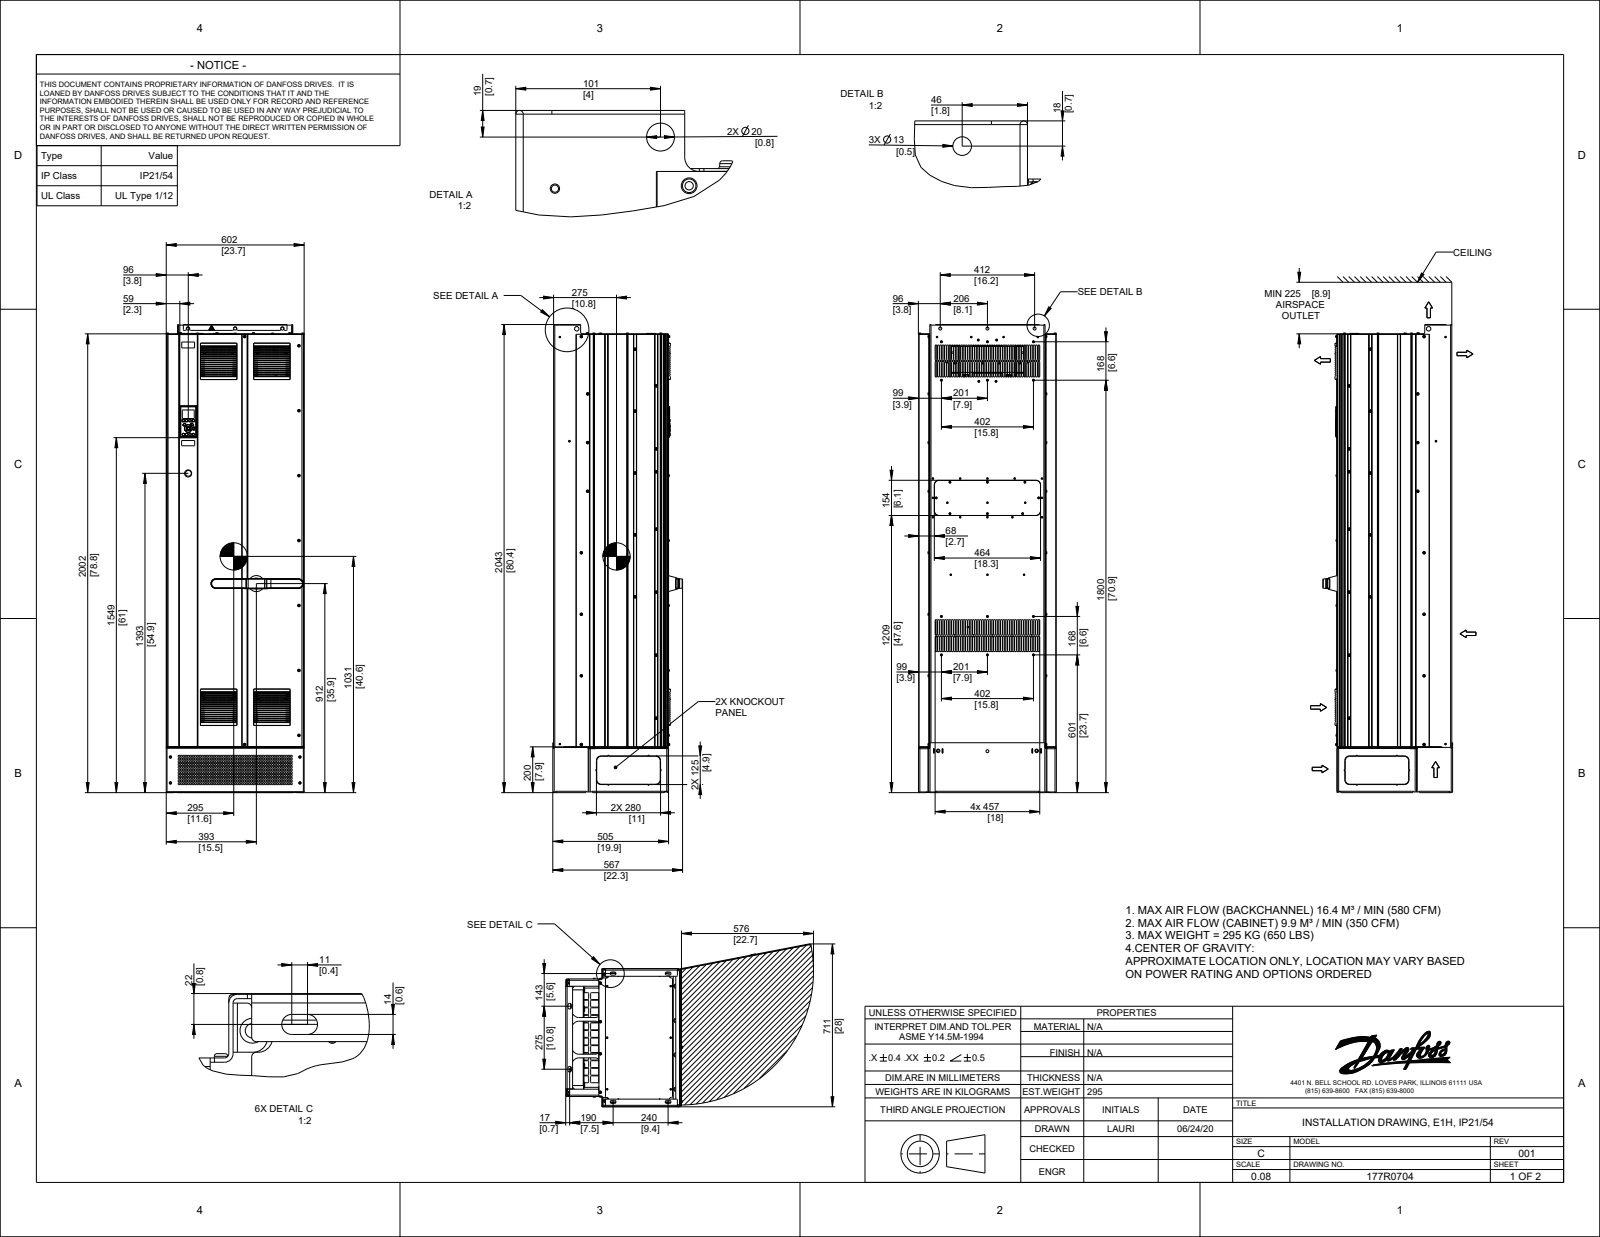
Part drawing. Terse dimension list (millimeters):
name: 177G8943; FH-M6-15-ZI; SS-M5-2-ZI; S-M6-2-ZI (+8 more)
written by: CREO PARAMETRIC BY PTC INC, 2015480 (CONFIG_CONTROL_DESIGN)
unit: mm
bodies: 600 solids, 39457 faces (23407 planar, 9063 cylindrical, 6987 other)
size: 2042.6 × 603 × 514.14
volume: 22 040 000 mm³; area: 17 500 000 mm²
holes: 148× ⌀5, 85× ⌀6, 40× ⌀6.33, 32× ⌀1.2, 30× ⌀5.8, 26× ⌀8, 21× ⌀6.5, 20× ⌀4, 19× ⌀5.5, 17× ⌀6.3, 16× ⌀1.5, 16× ⌀6.4
bosses: 83× ⌀6.5, 60× ⌀8.7, 49× ⌀10.8, 49× ⌀9.8, 46× ⌀12, 28× ⌀5, 26× ⌀11, 20× ⌀6.33
rounds: 456× R4, 369× R0.5, 325× R3.2, 243× R1, 134× R0.4, 122× R0.3, 105× R1.6, 86× R2
face distances: 3, 2.6, 494.36, 497.36, 496.96, 499.96, 597.1, 1.9, 6.4, 590.7
hole spacings: 83, 91.71, 200.9, 166, 170.52, 261.69, 1215.22, 39
